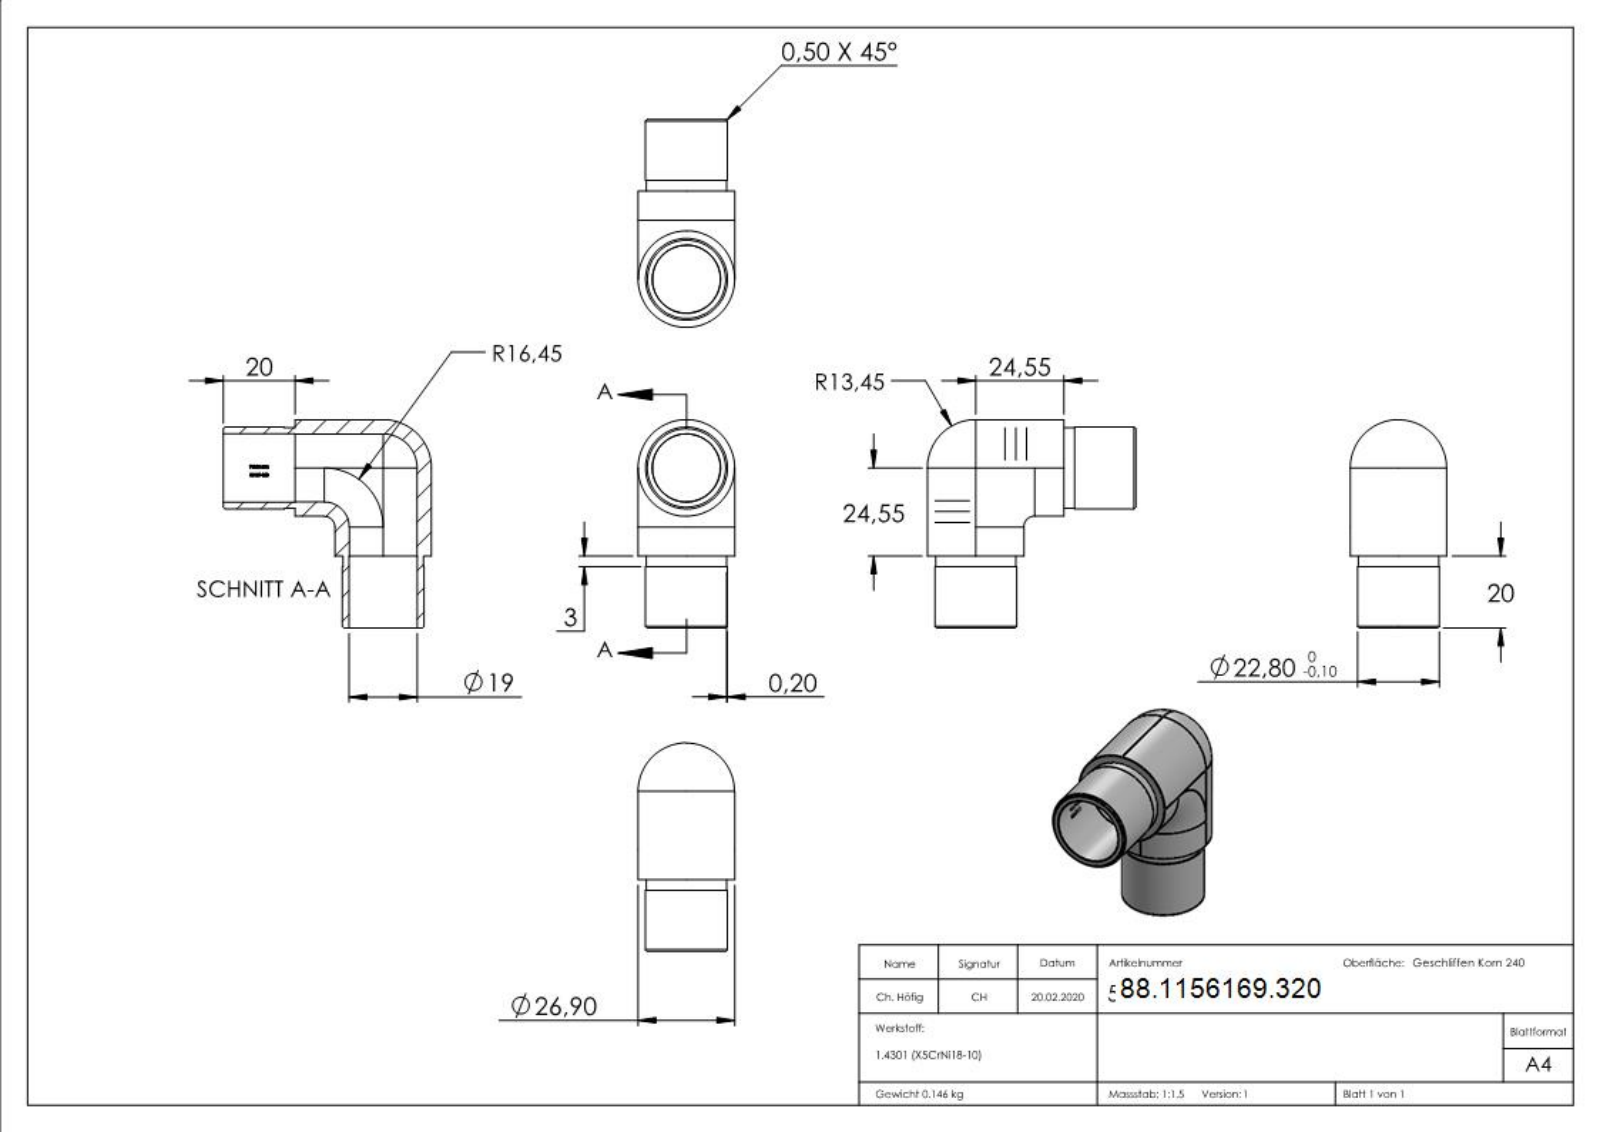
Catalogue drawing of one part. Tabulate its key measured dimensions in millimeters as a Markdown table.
| quantity | value |
| --- | --- |
| part name | 56169-320 |
| STEP written by | SolidWorks 2015 (CONFIG_CONTROL_DESIGN) |
| units | millimeters |
| bodies | 1 solid, 268 faces (100 planar, 46 cylindrical, 122 other) |
| overall size | 58 × 58 × 26.9 |
| volume | 18 465 mm³ |
| surface area | 12 630 mm² |
| round holes (diameter × count) | 18.9 × 2, 19 × 2 |
| round bosses / shafts (diameter × count) | 26.9 × 2, 22.8 × 2, 22.4 × 2 |
| partial cylindrical surfaces (radius × count) | 9.6 × 1 |
| main face-to-face distances | 20, 4, 22.9, 18.9, 26.9, 17, 3, 1.78, 0.83, 0.76 |
